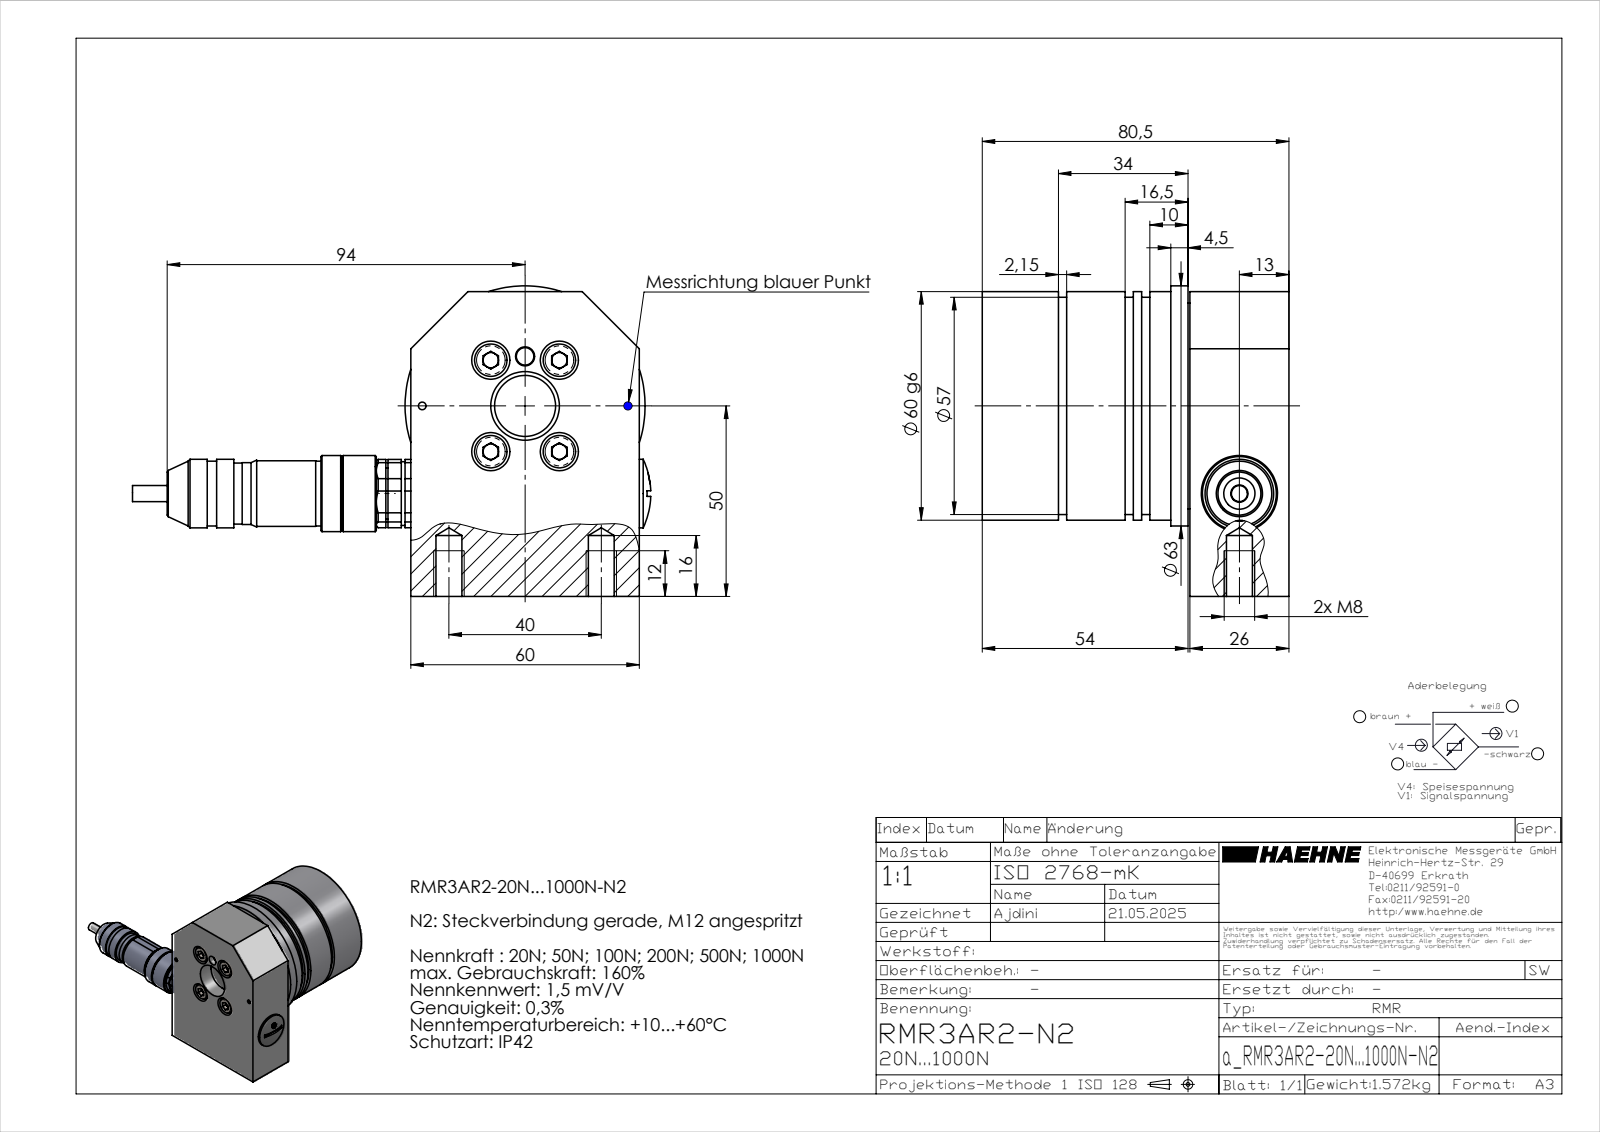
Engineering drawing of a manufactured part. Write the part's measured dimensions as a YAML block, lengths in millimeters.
part_name: "a_RMR3AR2-20N...1000N-N2"
step_written_by: "SolidWorks 2023 (AUTOMOTIVE_DESIGN)"
units: millimeters
bodies: {solids: 16, faces: 491, planar: 248, cylindrical: 156, other: 87}
overall_size: [136.04, 81.5, 80.5]
volume: 243343
surface_area: 74838
round_holes:
  - {diameter: 1, count: 5}
  - {diameter: 4.2, count: 4}
  - {diameter: 5.3, count: 4}
  - {diameter: 10, count: 4}
  - {diameter: 2, count: 2}
  - {diameter: 6.8, count: 2}
  - {diameter: 0.64, count: 1}
  - {diameter: 3, count: 1}
  - {diameter: 4.5, count: 1}
  - {diameter: 5, count: 1}
  - {diameter: 8.2, count: 1}
  - {diameter: 8.37, count: 1}
round_bosses_or_shafts:
  - {diameter: 0.86, count: 5}
  - {diameter: 8.5, count: 4}
  - {diameter: 5, count: 4}
  - {diameter: 1.5, count: 4}
  - {diameter: 1, count: 4}
  - {diameter: 63, count: 1}
  - {diameter: 60, count: 1}
  - {diameter: 57, count: 1}
partial_cylinders:
  - {radius: 0.3, count: 6}
  - {radius: 1, count: 4}
  - {radius: 0.57, count: 1}
  - {radius: 0.6, count: 1}
  - {radius: 0.77, count: 1}
  - {radius: 3.5, count: 1}
  - {radius: 24, count: 1}
  - {radius: 40, count: 1}
face_to_face_distances: [11.5, 48.5, 37, 73, 54.5, 62, 11, 47, 15, 26]
hole_center_spacings: [2.5, 3.54, 15, 21.63, 37.95, 5, 9.06, 18]
